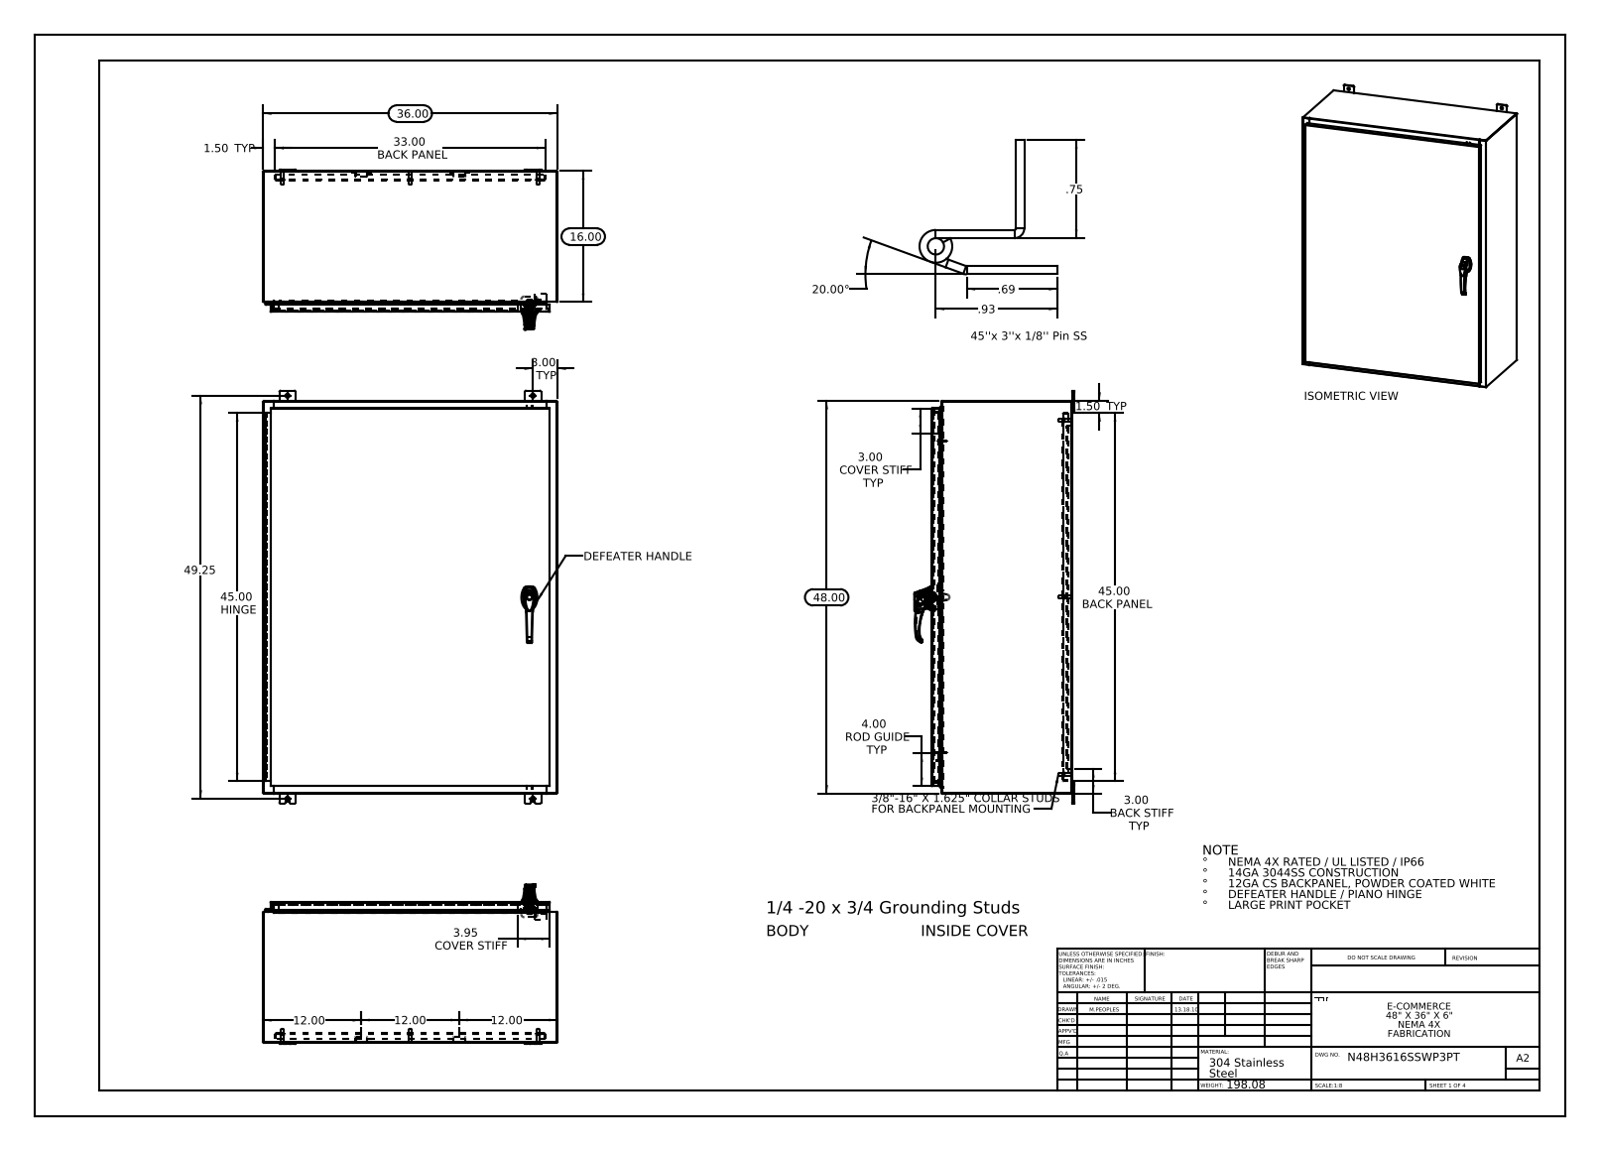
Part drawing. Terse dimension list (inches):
name: N48H3616SSWP3PT Body; 00005090; N48H3616SSWP3PT Defeater Handle Rod; 21130102 (+8 more)
written by: SolidWorks 2013 (CONFIG_CONTROL_DESIGN)
unit: in
bodies: 39 solids, 3224 faces (1273 planar, 1257 cylindrical, 694 other)
size: 50.5 × 36 × 19.495
volume: 706 in³; area: 17 647 in²
holes: 12× ⌀0.5, 10× ⌀0.25, 3× ⌀0.138, 3× ⌀0.161, 2× ⌀0.079, 2× ⌀0.203, 2× ⌀0.313, 2× ⌀0.437, 1× ⌀0.125, 1× ⌀0.125, 1× ⌀0.197, 1× ⌀0.276
bosses: 8× ⌀0.625, 8× ⌀0.375, 8× ⌀0.33, 1× ⌀1.181, 1× ⌀0.748, 1× ⌀0.68, 1× ⌀0.661, 1× ⌀0.639
rounds: 37× R0.118, 34× R0.013, 33× R0.006, 28× R0.088, 24× R0.19, 15× R0.039, 12× R0.028, 6× R0.008
face distances: 0.075, 17.126, 17.051, 17.201, 0.104, 35.925, 1, 16.126, 1.075, 16.051
hole spacings: 17.357, 19.665, 21.625, 38.003, 45.986, 31.25, 43.25, 0.295
